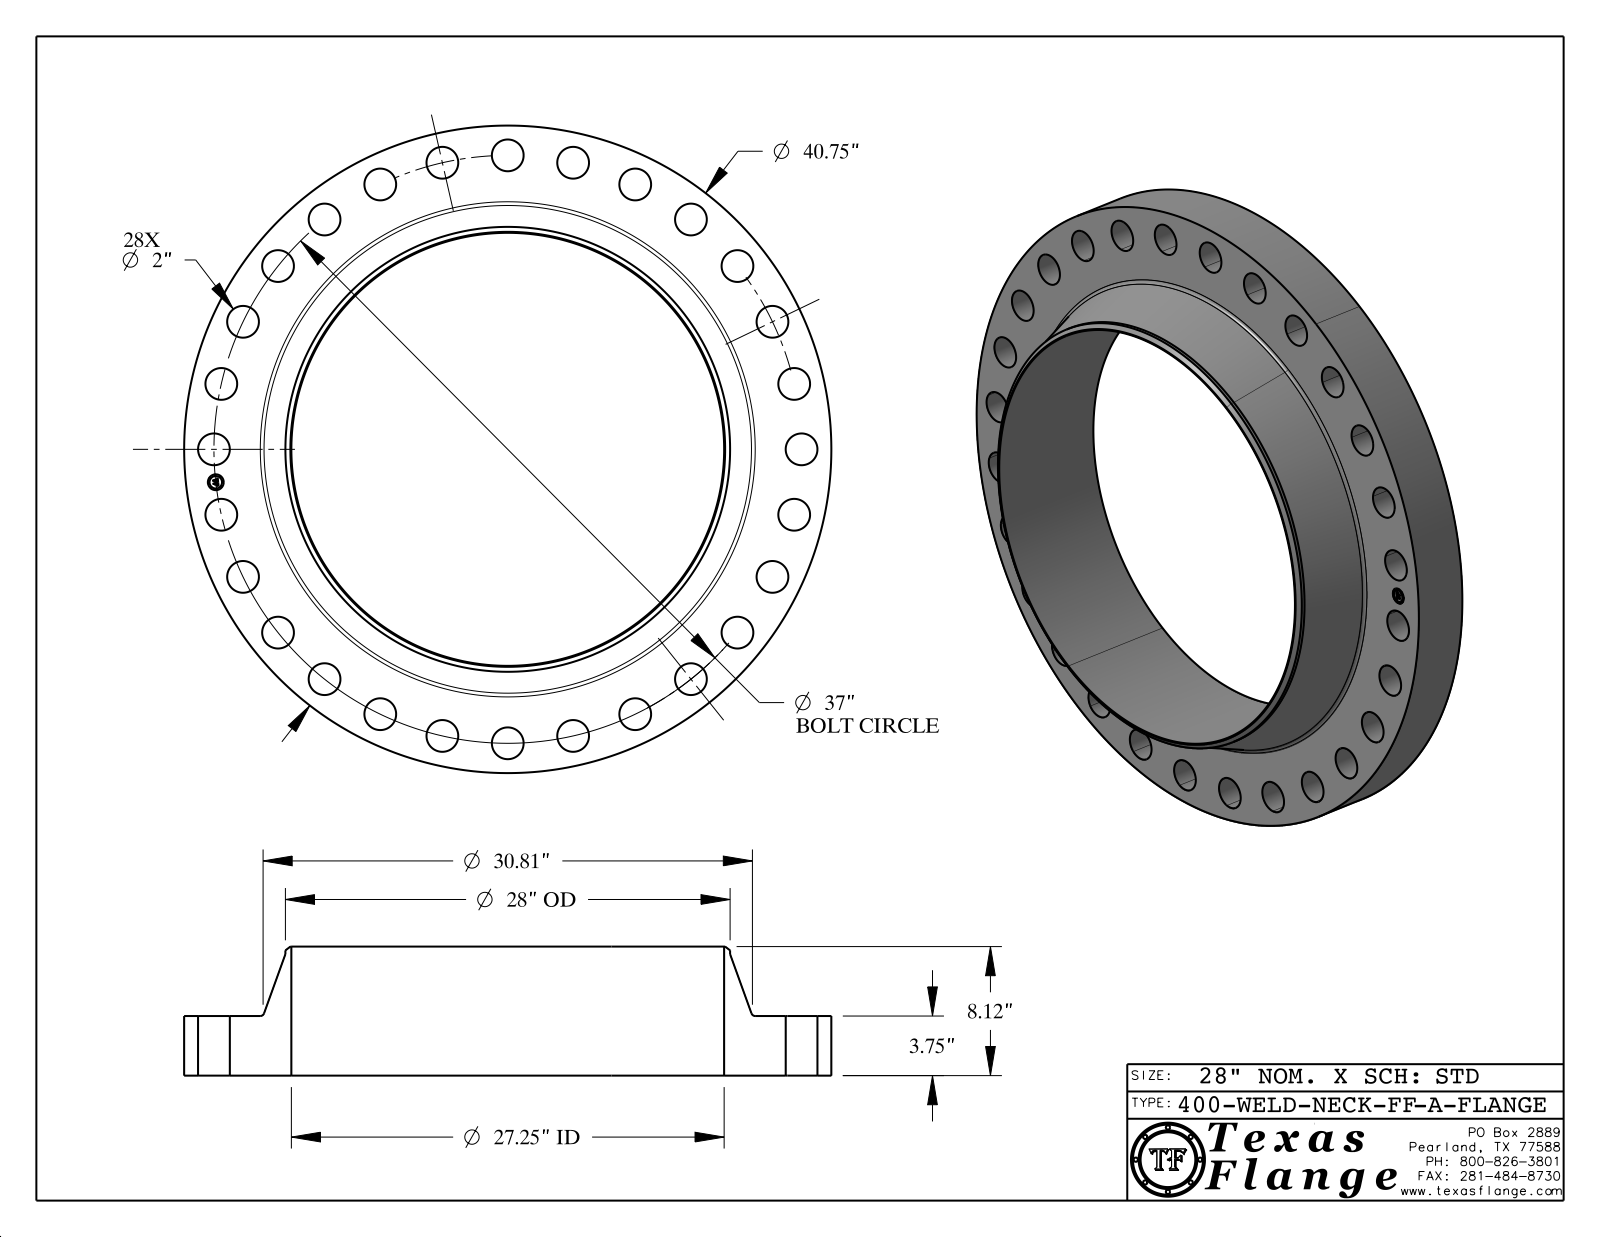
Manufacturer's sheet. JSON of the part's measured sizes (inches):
{"part_name": "400-WELD-NECK-FF, Series A", "step_written_by": "CATIA V5 STEP AP214 (AUTOMOTIVE_DESIGN)", "units": "inches", "bodies": {"solids": 1, "faces": 456, "planar": 368, "cylindrical": 82, "other": 6}, "overall_size": [40.75, 40.75, 8.12], "volume_in3": 2762, "surface_area_in2": 3377, "round_holes": [[2, 28], [1, 1], [27.25, 1]], "round_bosses_or_shafts": [[0.061, 8], [40.75, 1], [28, 1], [0.788, 1]], "face_to_face_distances": [3.75, 8.12, 4.37, 0.015, 3.735, 4.385, 0.298, 0.292, 0.054, 0.193], "hole_center_spacings": [18.5, 26.163, 31.329, 36.072, 36.767, 33.336, 4.143, 16.054]}
